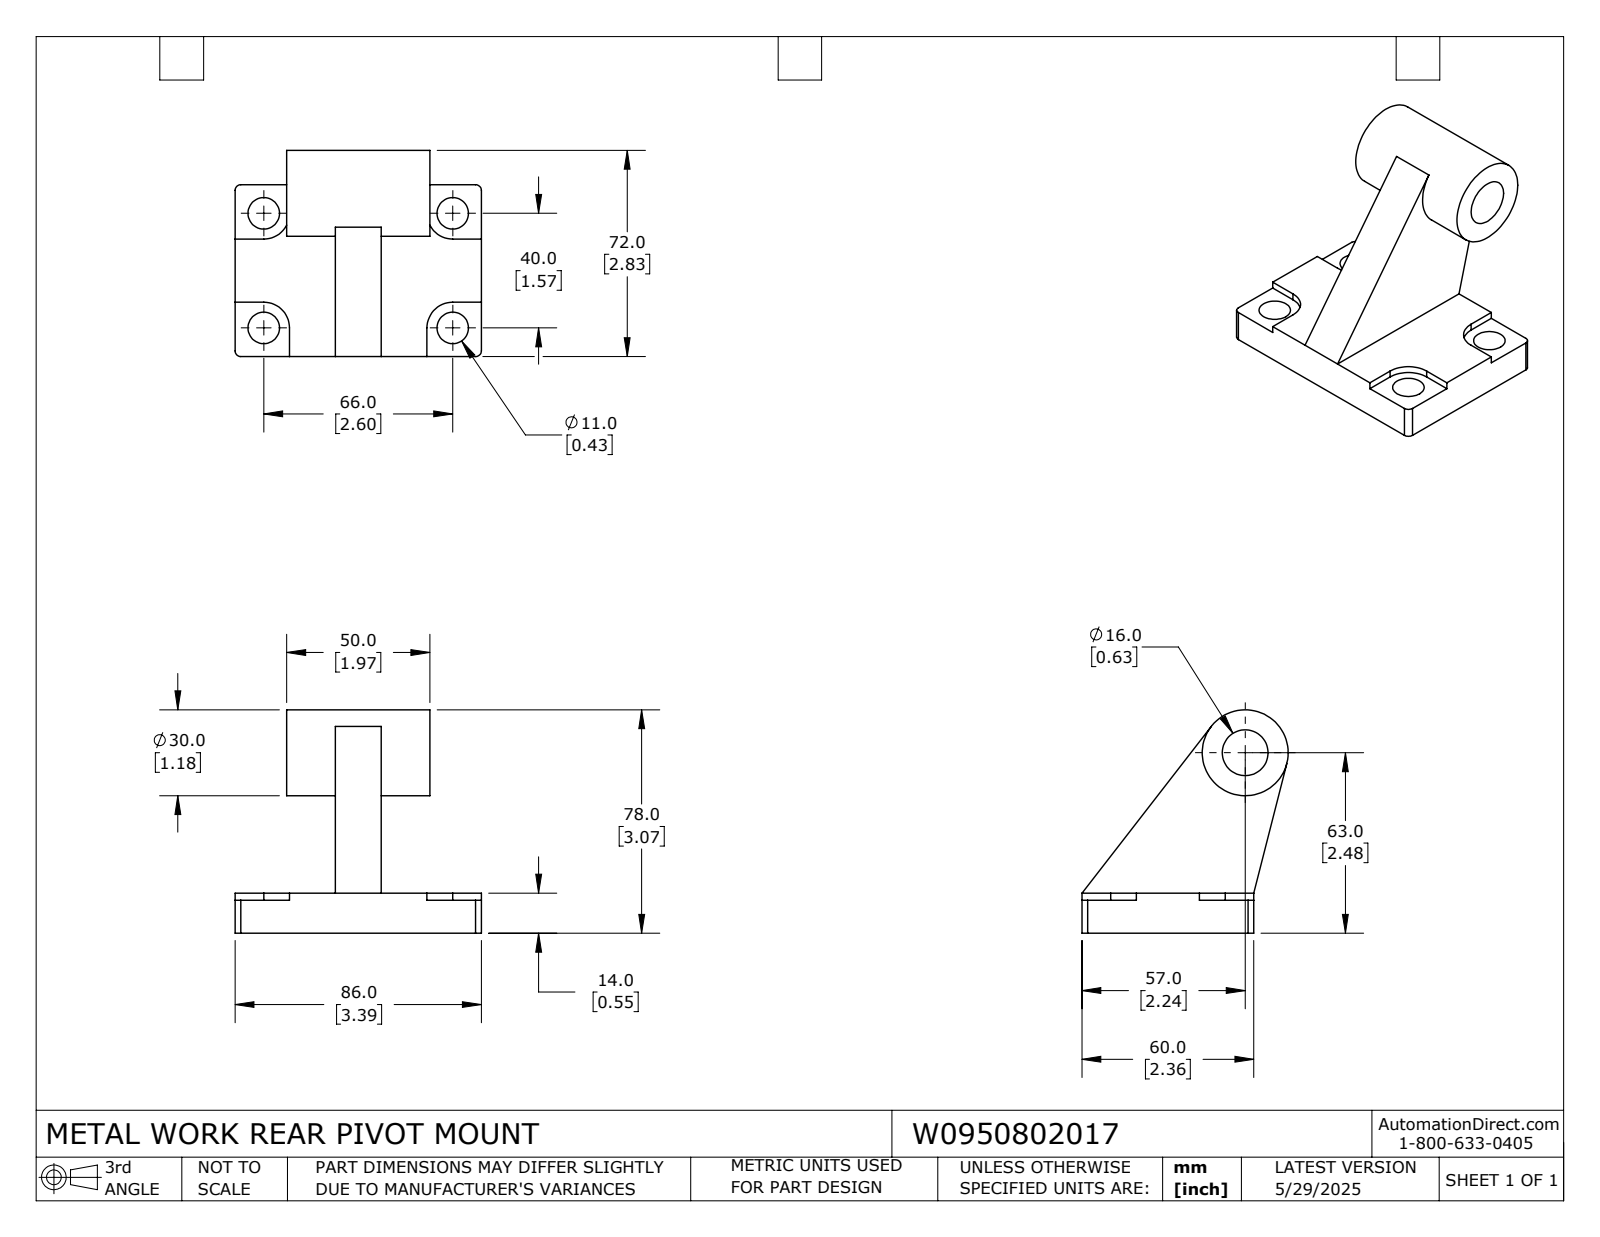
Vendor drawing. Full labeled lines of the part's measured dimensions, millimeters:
Part name (STEP PRODUCT): W0950802017
STEP written by: SolidWorks 2024 (CONFIG_CONTROL_DESIGN)
Units: millimetres
Bodies: 1 solid, 50 faces (30 planar, 20 cylindrical, 0 other)
Overall size (bounding box): 86 × 78 × 72
Volume: 119 934 mm³ · Surface area: 27 702 mm²
Round holes (diameter × count): ⌀11 ×4, ⌀16 ×1
Round bosses / shafts (diameter × count): ⌀30 ×1
Partial cylindrical surfaces — rounded edges, fillets, slot ends (radius × count): R2 ×4, R9 ×4
Main face-to-face distances: 14, 16, 35, 51, 2.5, 60, 18, 68, 17, 33
Hole centre spacings: 40, 66, 77.18
